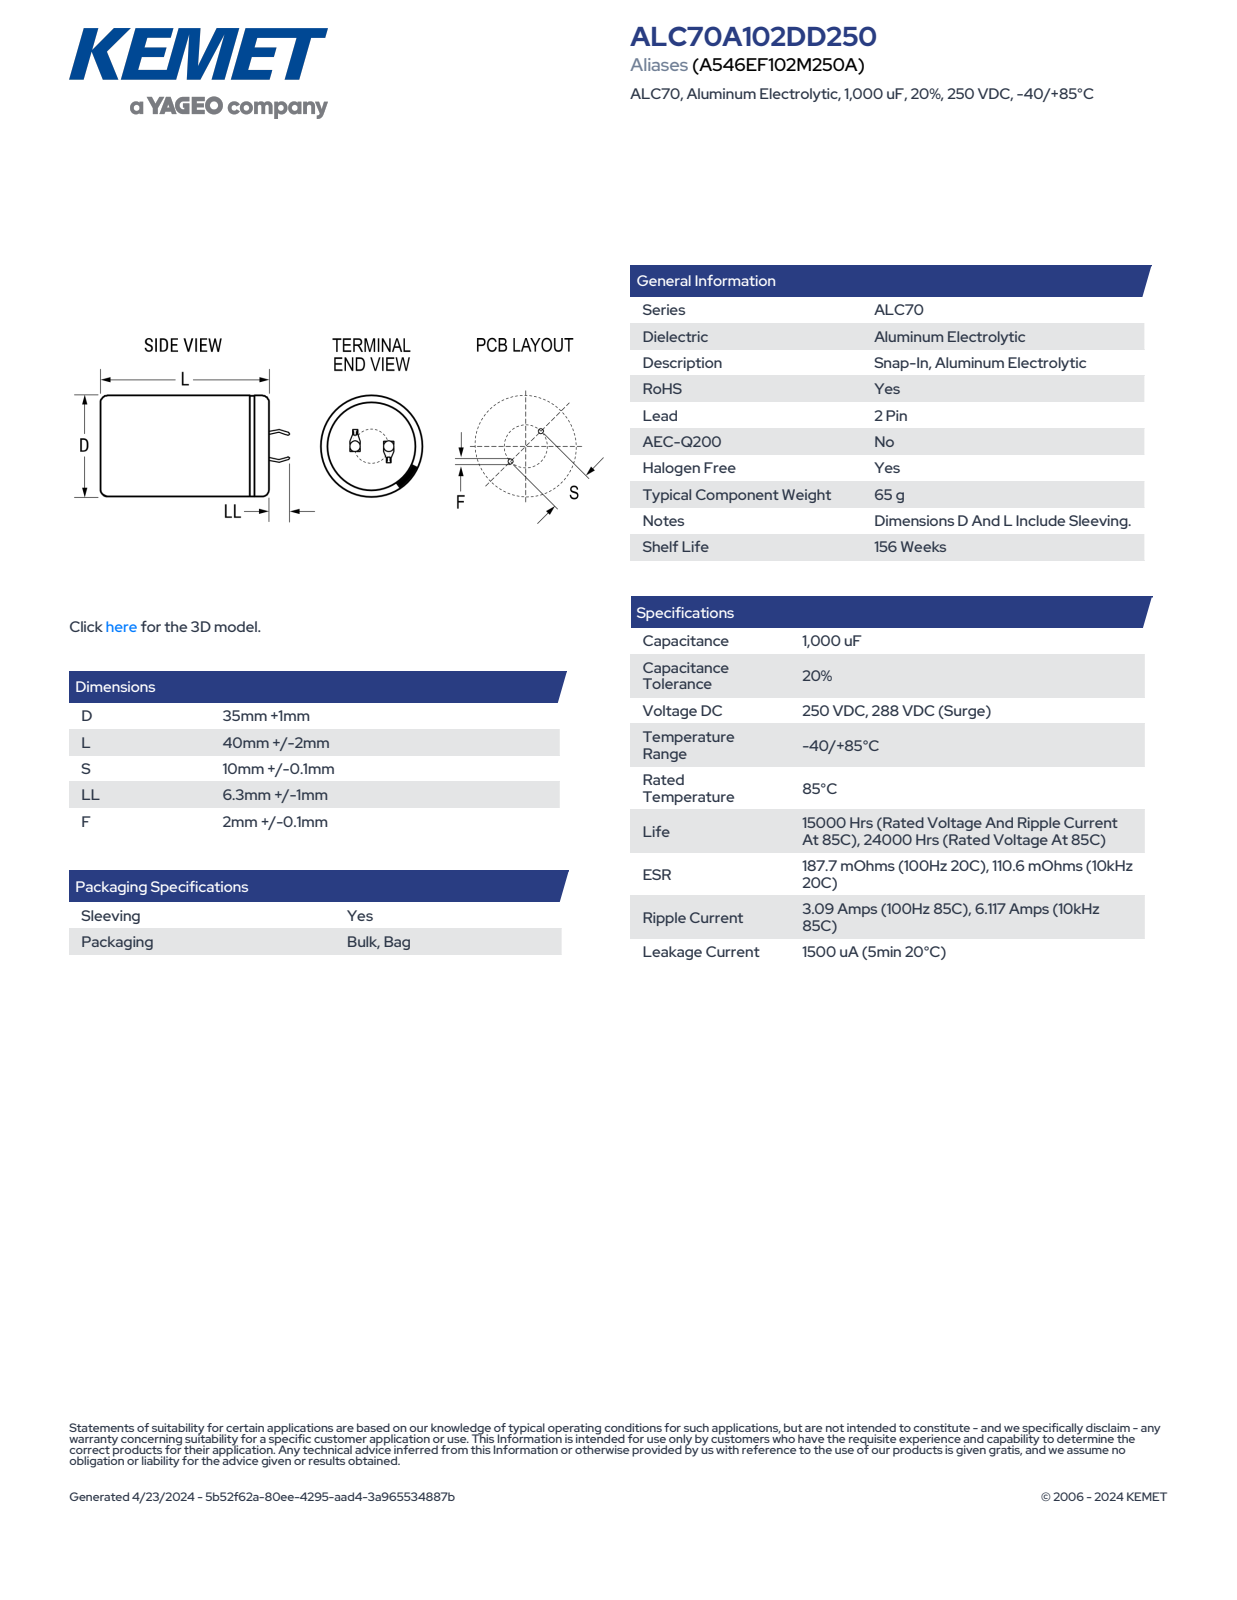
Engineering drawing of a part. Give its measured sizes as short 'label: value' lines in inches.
name: CARS_K2P_35X40_D36L42S10LL7.3F2.1
written by: SolidWorks 2014 (AUTOMOTIVE_DESIGN)
unit: in
bodies: 1 solid, 100 faces (52 planar, 9 cylindrical, 39 other)
size: 1.941 × 1.417 × 1.417
volume: 2.577 in³; area: 10.51 in²
holes: 1× ⌀1.254
bosses: 1× ⌀1.417
rounds: 1× R0.708
face distances: 1.653, 0.024, 1.673, 0.02, 0.279, 0.301, 0.03, 0.053, 0.302, 0.255
